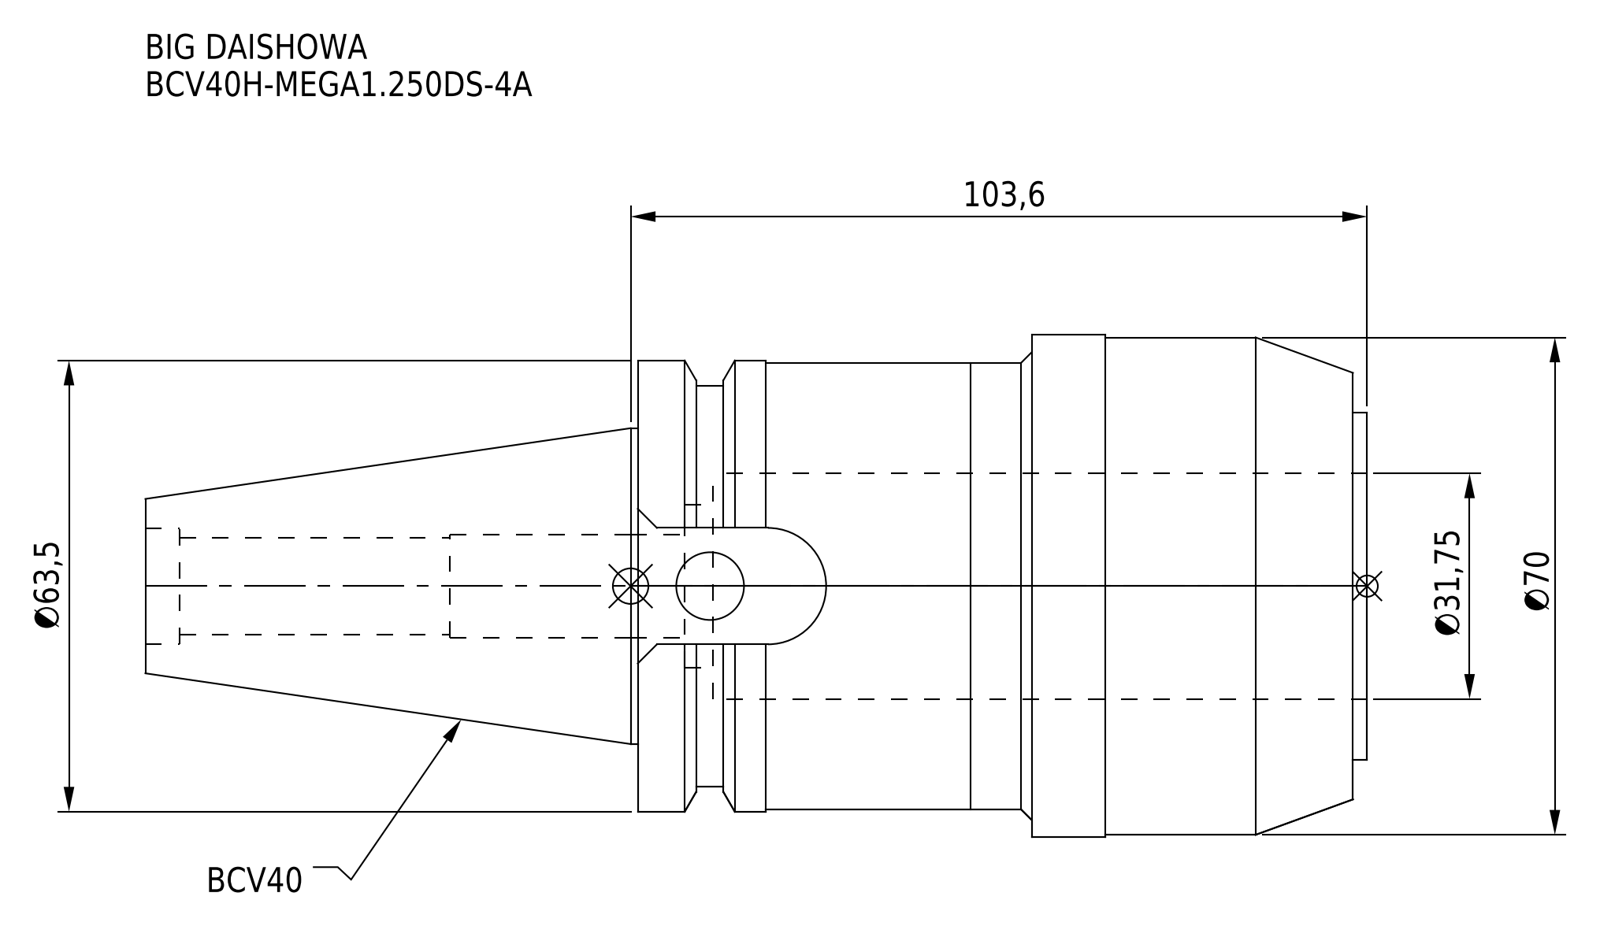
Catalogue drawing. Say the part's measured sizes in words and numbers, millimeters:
The part is named "BCV40H-MEGA1_250DS-4A". Its 3-D file was written by "CREO PARAMETRIC BY PTC INC, 2016380 (AUTOMOTIVE_DESIGN)". It is 1 solid with 69 faces: 27 planar, 32 cylindrical and 10 other. Overall it measures 171.85 by 70.7 by 70.7 millimeters. Its volume is 315 980 cubic millimeters and its surface area 48 203 square millimeters. Round holes: 1 of diameter 9.53, 1 of diameter 13.6, 1 of diameter 14.5, 1 of diameter 16.32, 1 of diameter 23, 1 of diameter 31.75. Round bosses or shafts: 1 of diameter 70.7, 1 of diameter 70, 1 of diameter 63.5, 1 of diameter 62.8, 1 of diameter 56.36, 1 of diameter 48.9, 1 of diameter 44.45. Partial cylindrical surfaces (rounded edges, fillets, slot ends): 1 of radius 8.19. The main face-to-face distances are 102.6, 2, 100.6, 47.2, 45.2, 55.4, 92, 90, 44.8, 10.6.
